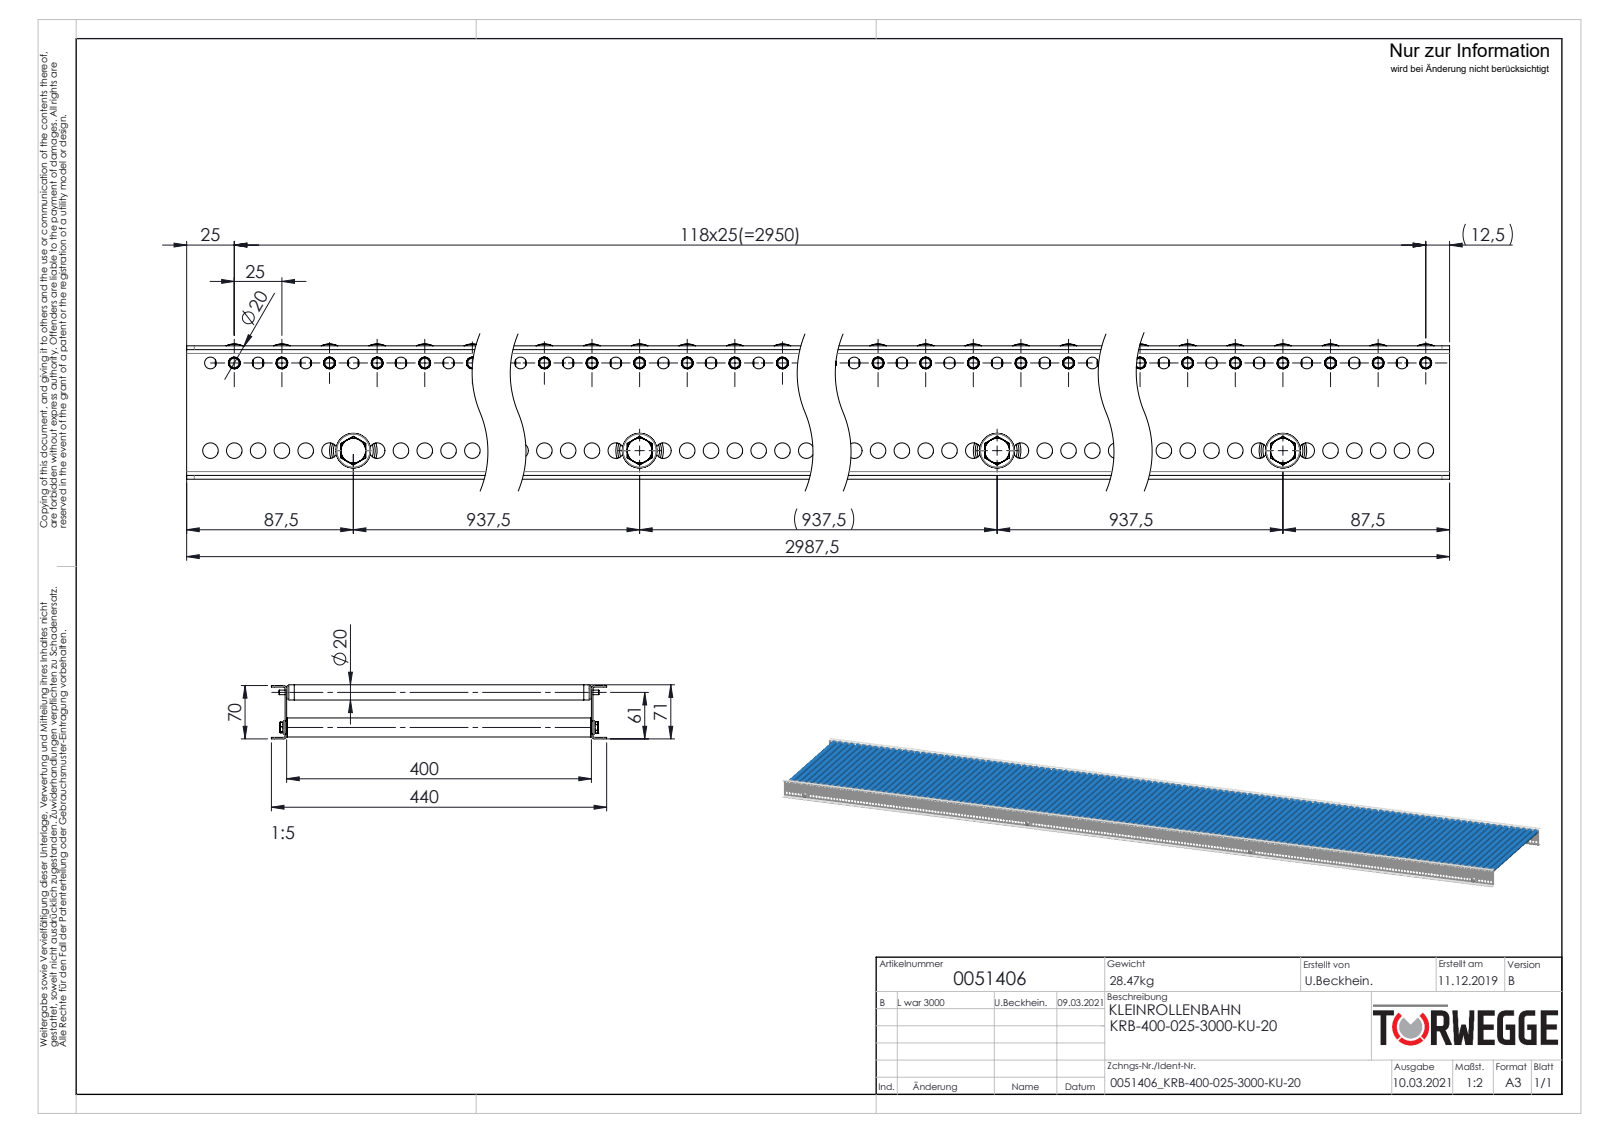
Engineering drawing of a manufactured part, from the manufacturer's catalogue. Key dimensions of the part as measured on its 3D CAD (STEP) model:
Part name (STEP PRODUCT): 0051406; 0039777_Achse-Ø06-FA-KFG_L=420 fr D20; KUT50-20x1,5-KU-A6_FA-EL=KFG_L=400; Traversen_KFG_L400 (+4 more)
STEP written by: SolidWorks 2020 (AUTOMOTIVE_DESIGN)
Units: millimetres
Bodies: 736 solids, 31448 faces (10438 planar, 11758 cylindrical, 9252 other)
Overall size (bounding box): 2987.5 × 440 × 71
Volume: 7 617 000 mm³ · Surface area: 8 725 000 mm²
Round holes (diameter × count): ⌀6.2 ×238, ⌀8.2 ×238, ⌀6.1 ×119, ⌀12.4 ×119, ⌀13.2 ×119, ⌀14.6 ×119, ⌀16.2 ×119, ⌀17 ×119, ⌀17.2 ×119, ⌀6.8 ×4, ⌀21 ×4
Round bosses / shafts (diameter × count): ⌀20 ×119, ⌀19.9 ×119, ⌀17.1 ×119, ⌀16.8 ×119, ⌀16.5 ×119, ⌀11.4 ×119, ⌀11.1 ×119, ⌀10.2 ×119
Partial cylindrical surfaces — rounded edges, fillets, slot ends (radius × count): R4.05 ×119, R4 ×8, R2 ×4
Main face-to-face distances: 2, 402, 68, 400, 404, 70, 66, 392, 10, 12
Hole centre spacings: 12.5, 25, 37.5, 50, 62.5, 75, 87.5, 100
